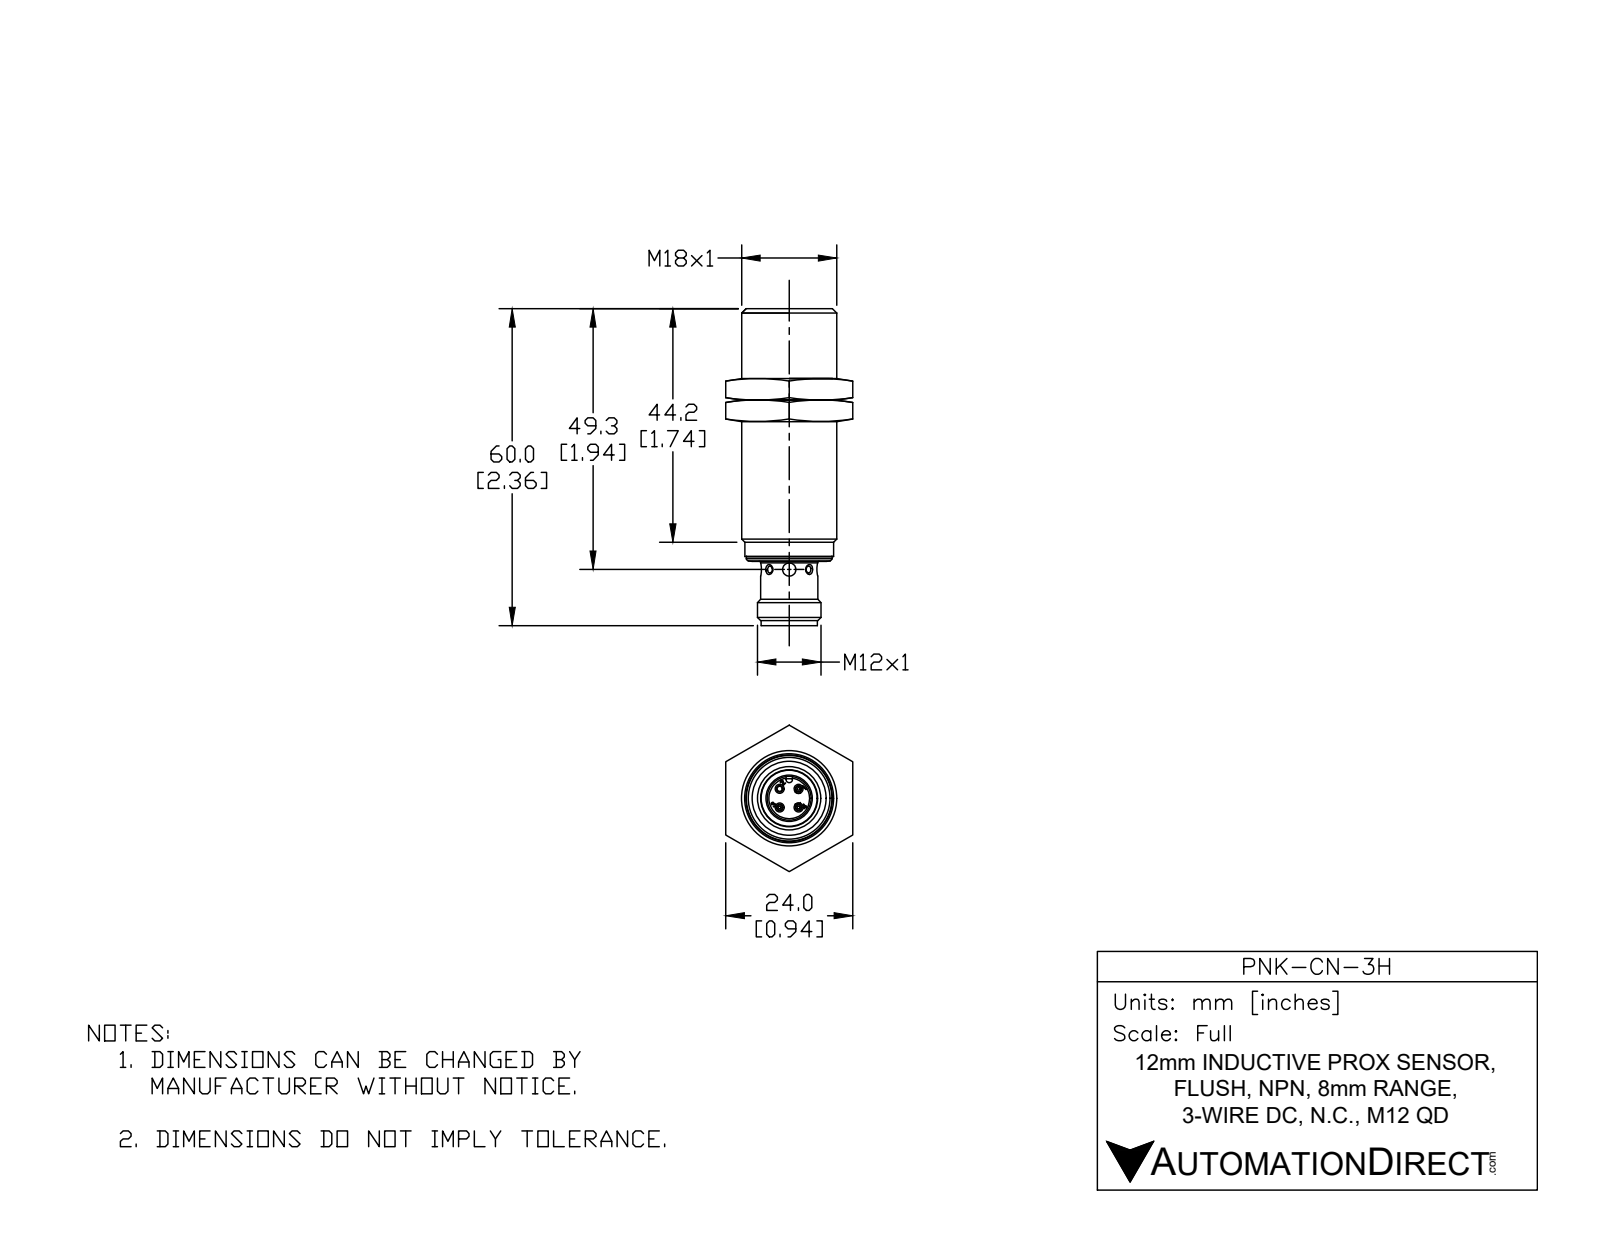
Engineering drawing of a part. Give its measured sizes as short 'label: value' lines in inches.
name: PNK-CN-3H
written by: SolidWorks 2017 (AUTOMOTIVE_DESIGN)
unit: in
bodies: 1 solid, 1142 faces (751 planar, 150 cylindrical, 241 other)
size: 2.362 × 0.709 × 0.709
volume: 0.746 in³; area: 14.66 in²
holes: 3× ⌀0.043, 2× ⌀0.04, 2× ⌀0.098, 1× ⌀0.038, 1× ⌀0.04, 1× ⌀0.327, 1× ⌀0.394, 1× ⌀0.618, 1× ⌀0.634
bosses: 9× ⌀0.039, 1× ⌀0.709, 1× ⌀0.654, 1× ⌀0.638, 1× ⌀0.633, 1× ⌀0.616, 1× ⌀0.608, 1× ⌀0.599
rounds: 38× R0.004, 1× R0.024, 1× R0.031, 1× R0.161
face distances: 0.039, 0.022, 0.018, 1.87, 1.882, 1.86, 1.843, 1.848, 1.831, 2.323
hole spacings: 0.098, 0.139, 0.197
